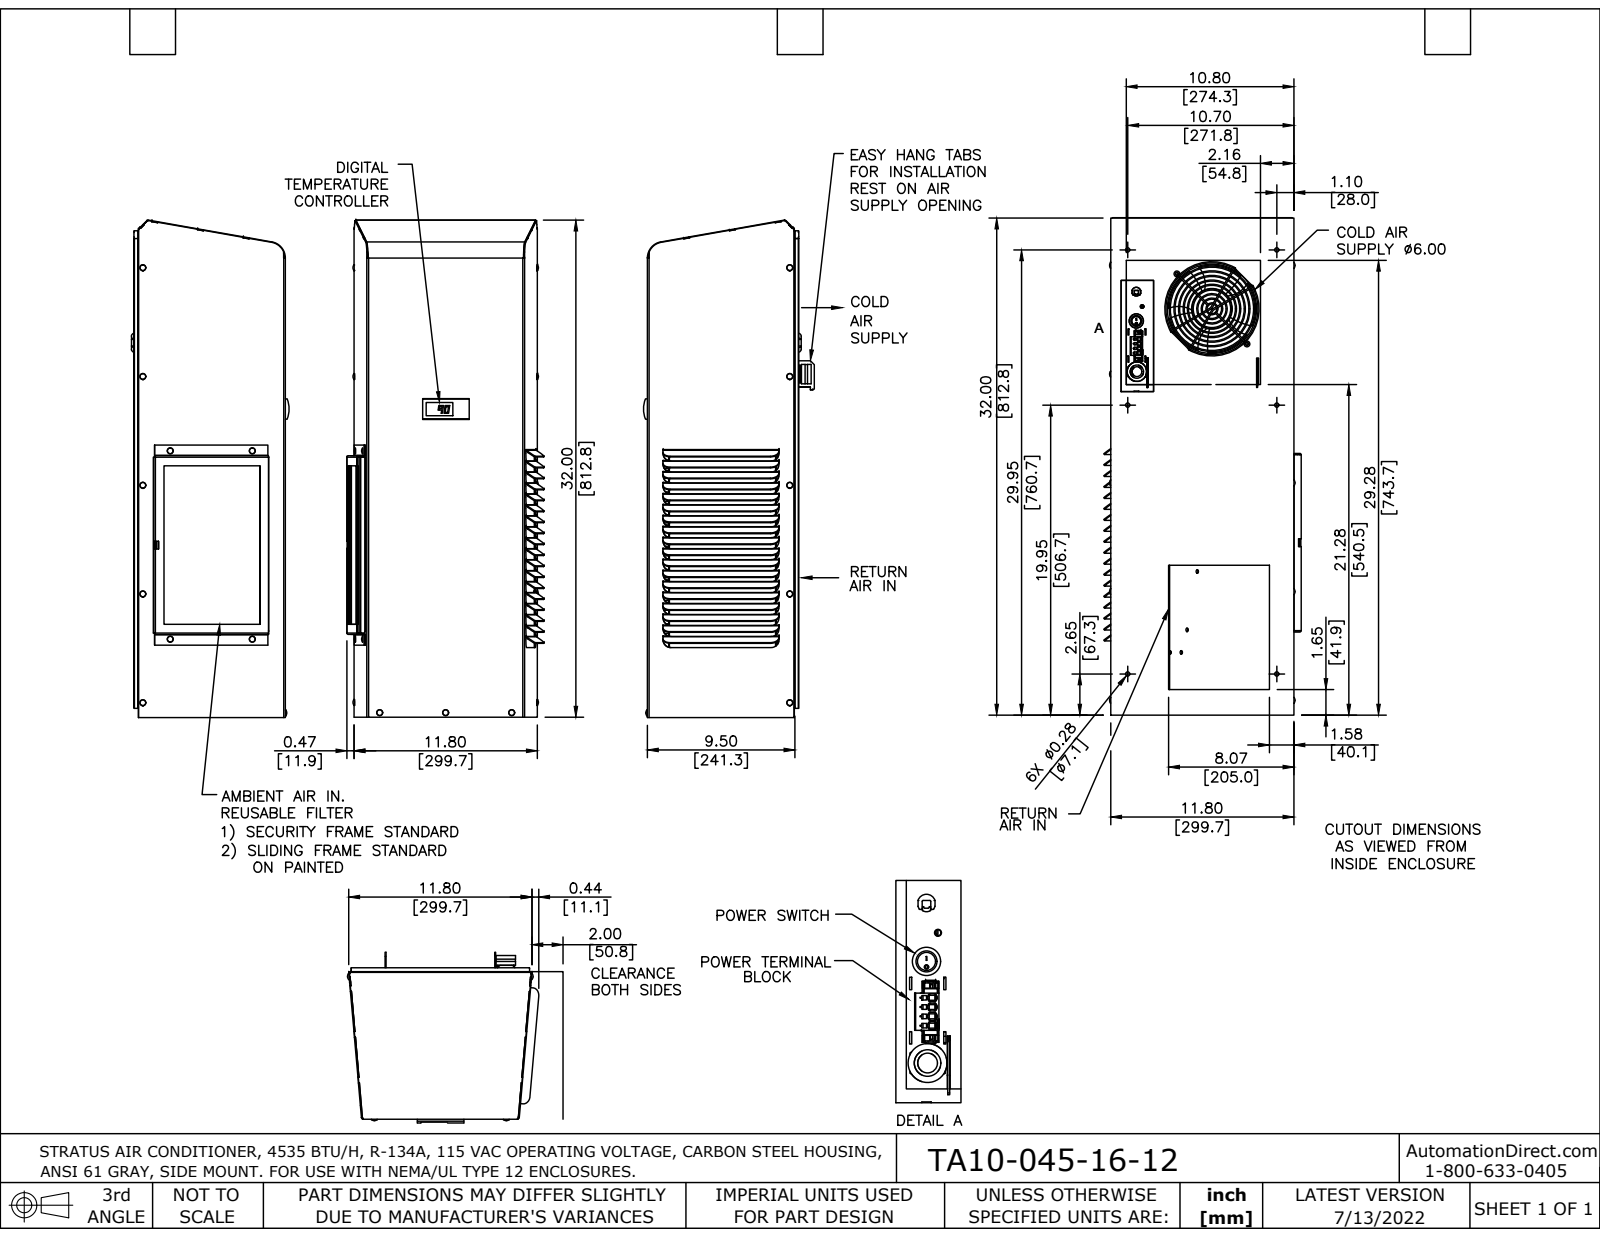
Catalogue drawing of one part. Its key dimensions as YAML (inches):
part_name: "TA10-045-16-12"
step_written_by: "SolidWorks 2021 (AUTOMOTIVE_DESIGN)"
units: inches
bodies: {solids: 1, faces: 1957, planar: 1208, cylindrical: 568, other: 181}
overall_size: [32.024, 12.576, 11.554]
volume: 144.6
surface_area: 3628
round_holes:
  - {diameter: 0.194, count: 17}
  - {diameter: 0.219, count: 15}
  - {diameter: 0.159, count: 11}
  - {diameter: 0.204, count: 5}
  - {diameter: 0.099, count: 3}
  - {diameter: 0.4, count: 2}
  - {diameter: 0.136, count: 1}
  - {diameter: 6, count: 1}
round_bosses_or_shafts:
  - {diameter: 0.19, count: 7}
  - {diameter: 0.379, count: 2}
  - {diameter: 0.353, count: 2}
  - {diameter: 0.248, count: 2}
  - {diameter: 6.07, count: 1}
  - {diameter: 0.906, count: 1}
  - {diameter: 0.087, count: 1}
partial_cylinders:
  - {radius: 0.015, count: 45}
  - {radius: 0.01, count: 42}
  - {radius: 0.5, count: 36}
  - {radius: 0.506, count: 36}
  - {radius: 0.1, count: 28}
  - {radius: 0.058, count: 21}
  - {radius: 0.116, count: 21}
  - {radius: 0.032, count: 15}
face_to_face_distances: [0.058, 9.377, 9.435, 9.431, 0.054, 9.489, 0.037, 0.058, 0.373, 0.254]
hole_center_spacings: [7, 14, 5.4, 7.068, 8.894, 21, 0.524, 2.861]
